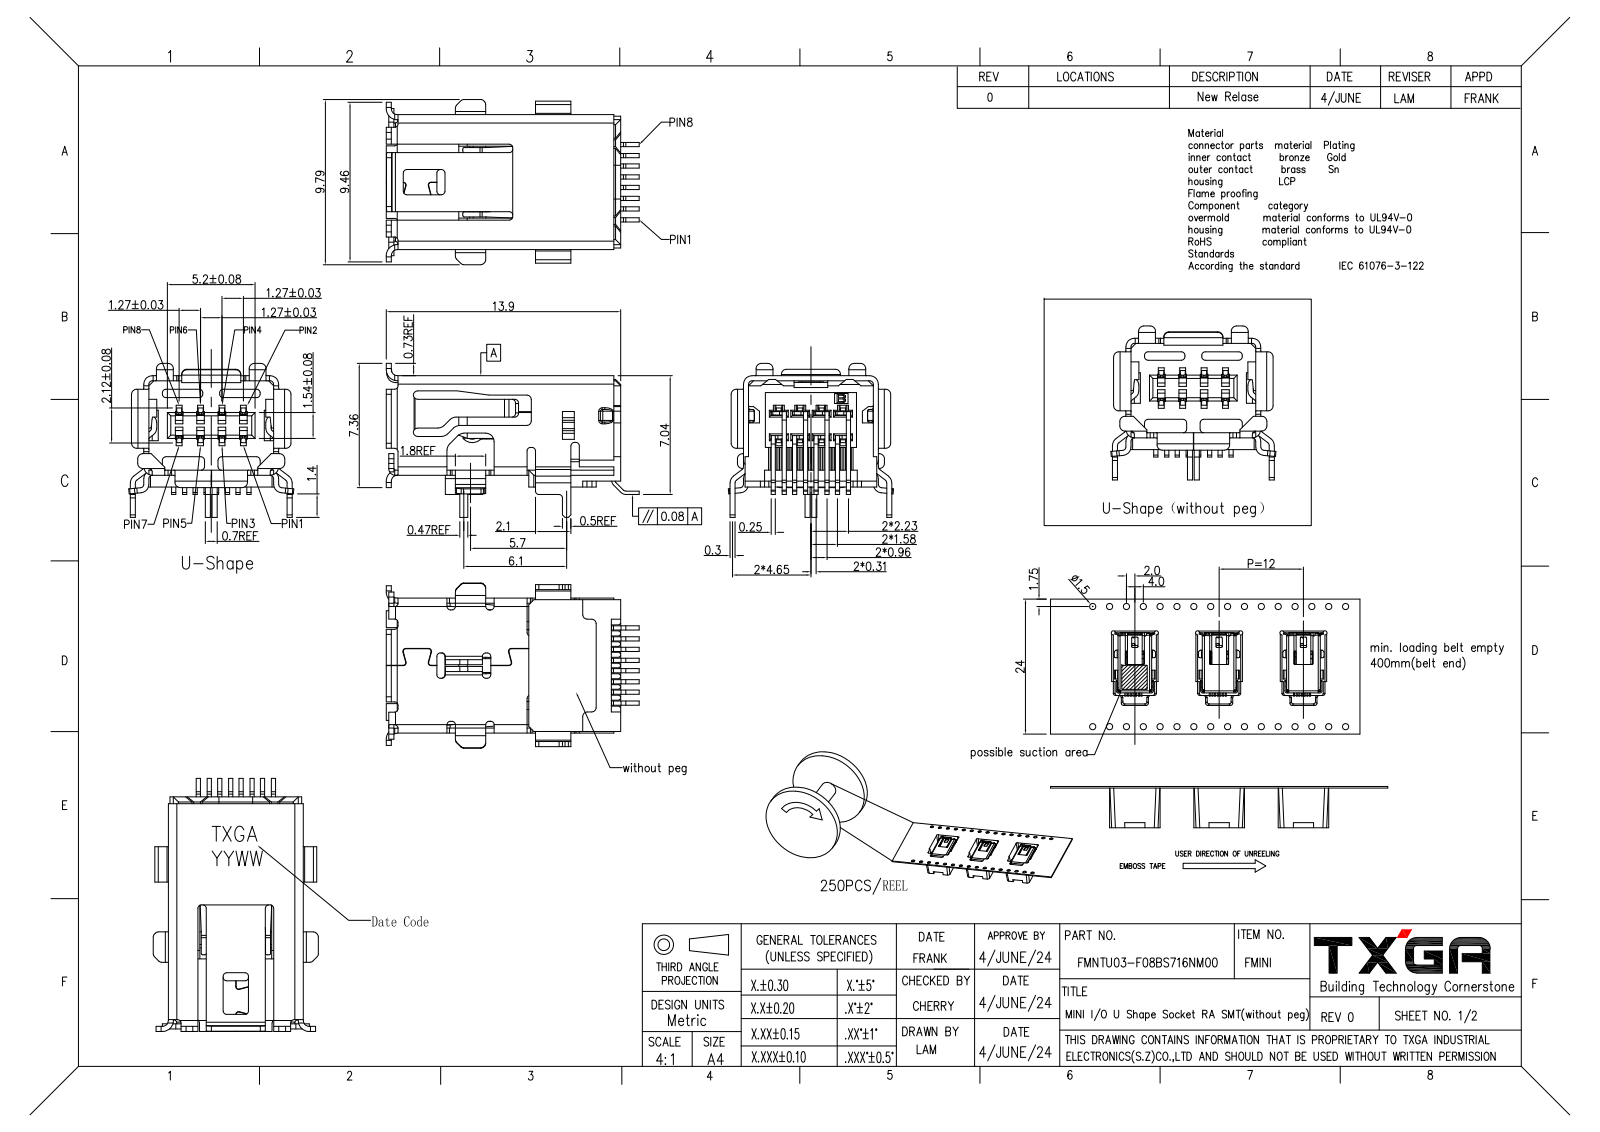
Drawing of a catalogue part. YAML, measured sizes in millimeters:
part_name: "FMINI-SURA0XXX-000"
step_written_by: "PRO/ENGINEER BY PARAMETRIC TECHNOLOGY CORPORATION, 2010280 (CONFIG_CONTROL_DESIGN)"
units: millimeters
bodies: {solids: 1, faces: 1549, planar: 1141, cylindrical: 384, other: 24}
overall_size: [15, 9.79, 9.13]
volume: 184
surface_area: 1236
partial_cylinders:
  - {radius: 0.2, count: 91}
  - {radius: 0.1, count: 65}
  - {radius: 0.5, count: 30}
  - {radius: 0.15, count: 24}
  - {radius: 0.3, count: 20}
  - {radius: 0.25, count: 12}
  - {radius: 0.4, count: 9}
  - {radius: 0.17, count: 8}
face_to_face_distances: [5.6, 5.3, 7.7, 5.9, 1, 6.6, 6.3, 8, 0.7, 7.4]
